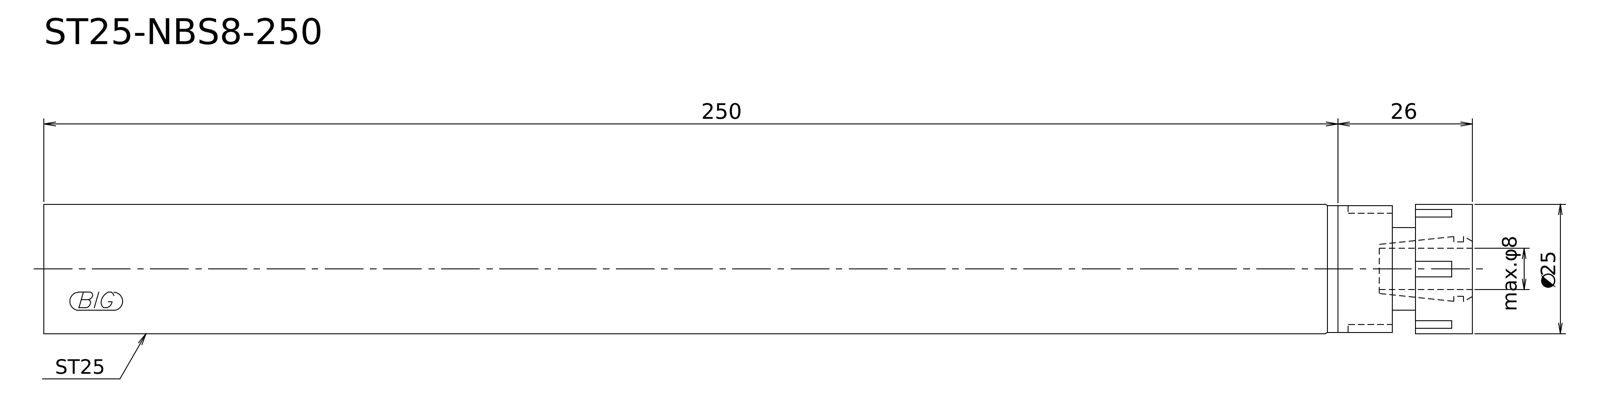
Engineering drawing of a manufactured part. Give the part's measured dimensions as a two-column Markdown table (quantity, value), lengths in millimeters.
| quantity | value |
| --- | --- |
| STEP written by | Kubotek KeyCreator V8.5.1 (14335) (CONFIG_CONTROL_DESIGN) |
| units | millimeters |
| bodies | 1 solid, 9 faces (5 planar, 4 cylindrical, 0 other) |
| overall size | 276 × 25 × 25 |
| volume | 133 927 mm³ |
| surface area | 23 091 mm² |
| round bosses / shafts (diameter × count) | 25 × 1, 24.5 × 1, 16 × 1 |
| main face-to-face distances | 276, 11, 265, 15.5, 4.5, 260.5, 28.35, 17.35, 12.85, 247.65 |
